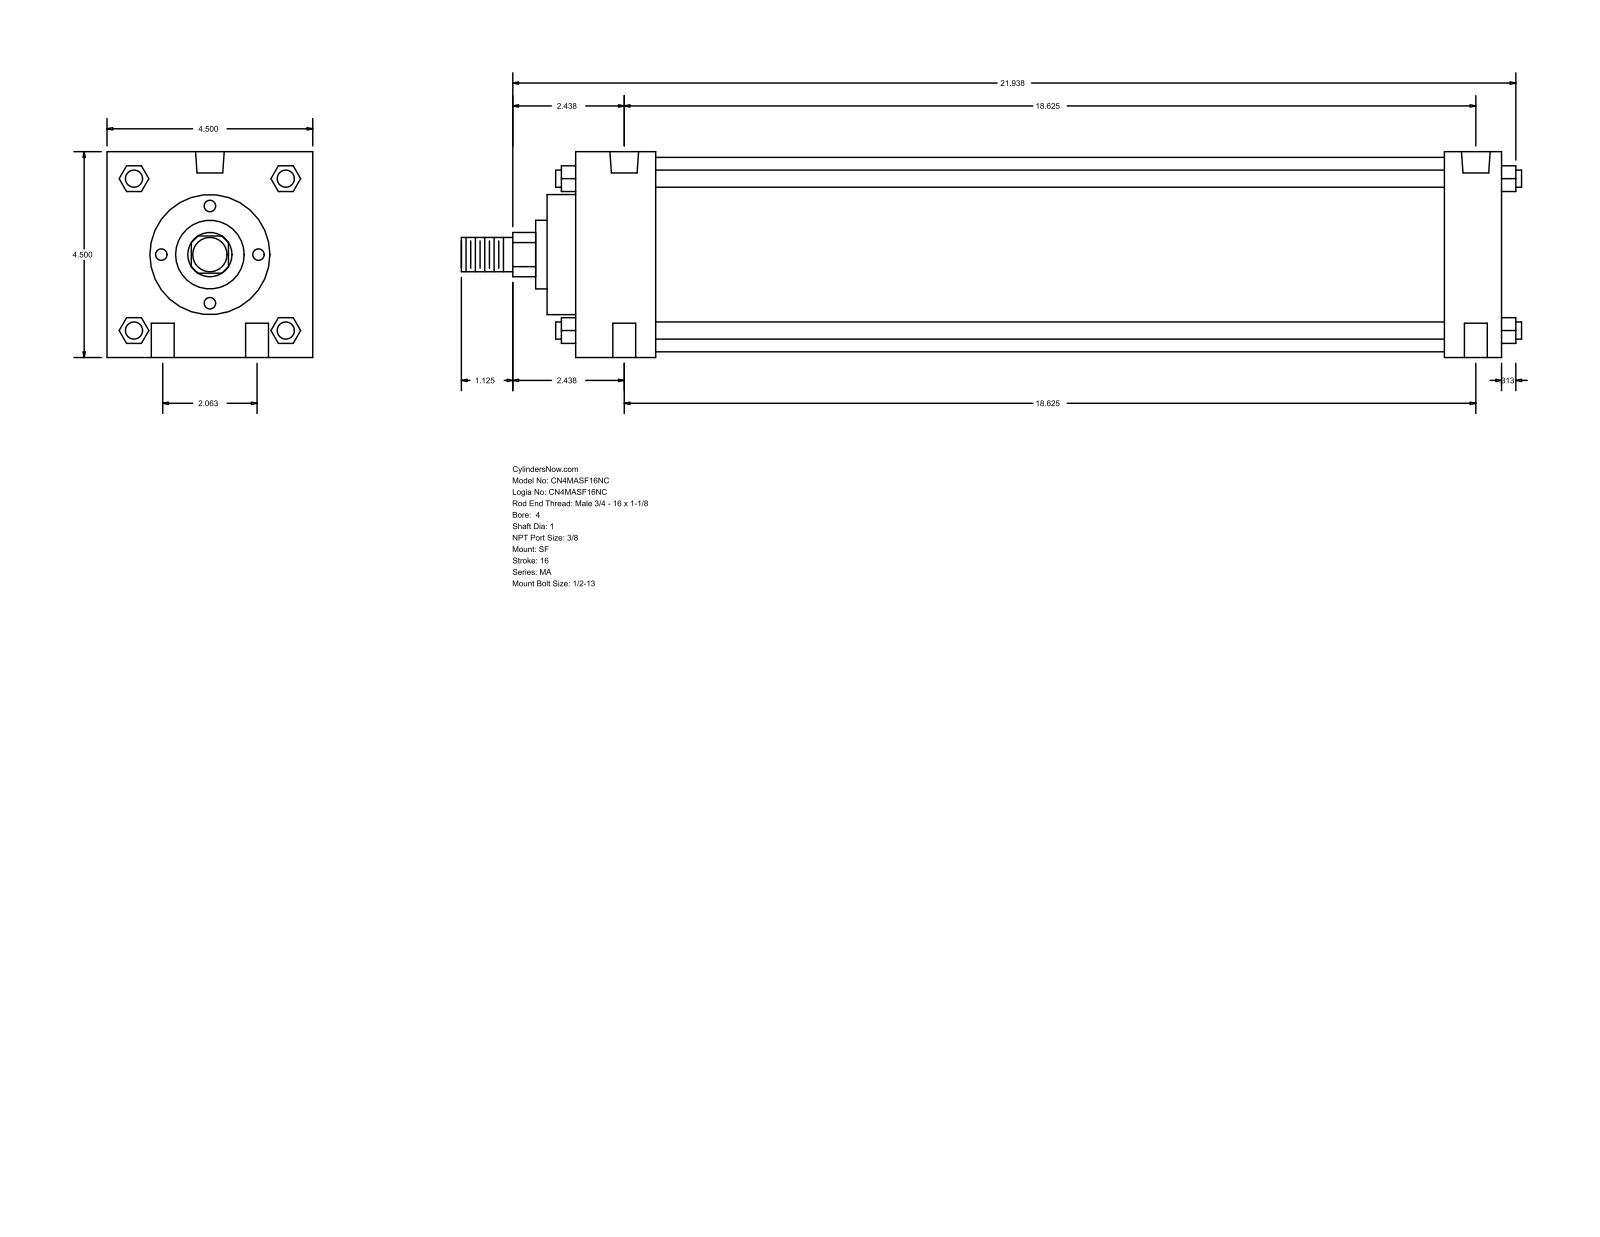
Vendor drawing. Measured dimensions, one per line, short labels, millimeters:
name: MA_SF__0400_1
written by: GSSL Pune (CONFIG_CONTROL_DESIGN)
unit: mm
bodies: 0 solids, 126 faces (95 planar, 31 cylindrical, 0 other)
size: 588.96 × 114.3 × 114.3
holes: 4× ⌀12.7, 2× ⌀11.11, 2× ⌀15.93
bosses: 4× ⌀9.53, 1× ⌀107.95, 1× ⌀66.67, 1× ⌀38.1, 1× ⌀25.4, 1× ⌀19.05
rounds: 1× R12.29
face distances: 114.3, 514.35, 482.6, 31.75, 44.46, 438.14, 469.89, 530.22, 15.87, 60.33
hole spacings: 26.19, 473.8, 473.08, 52.38, 475.97, 463.56
